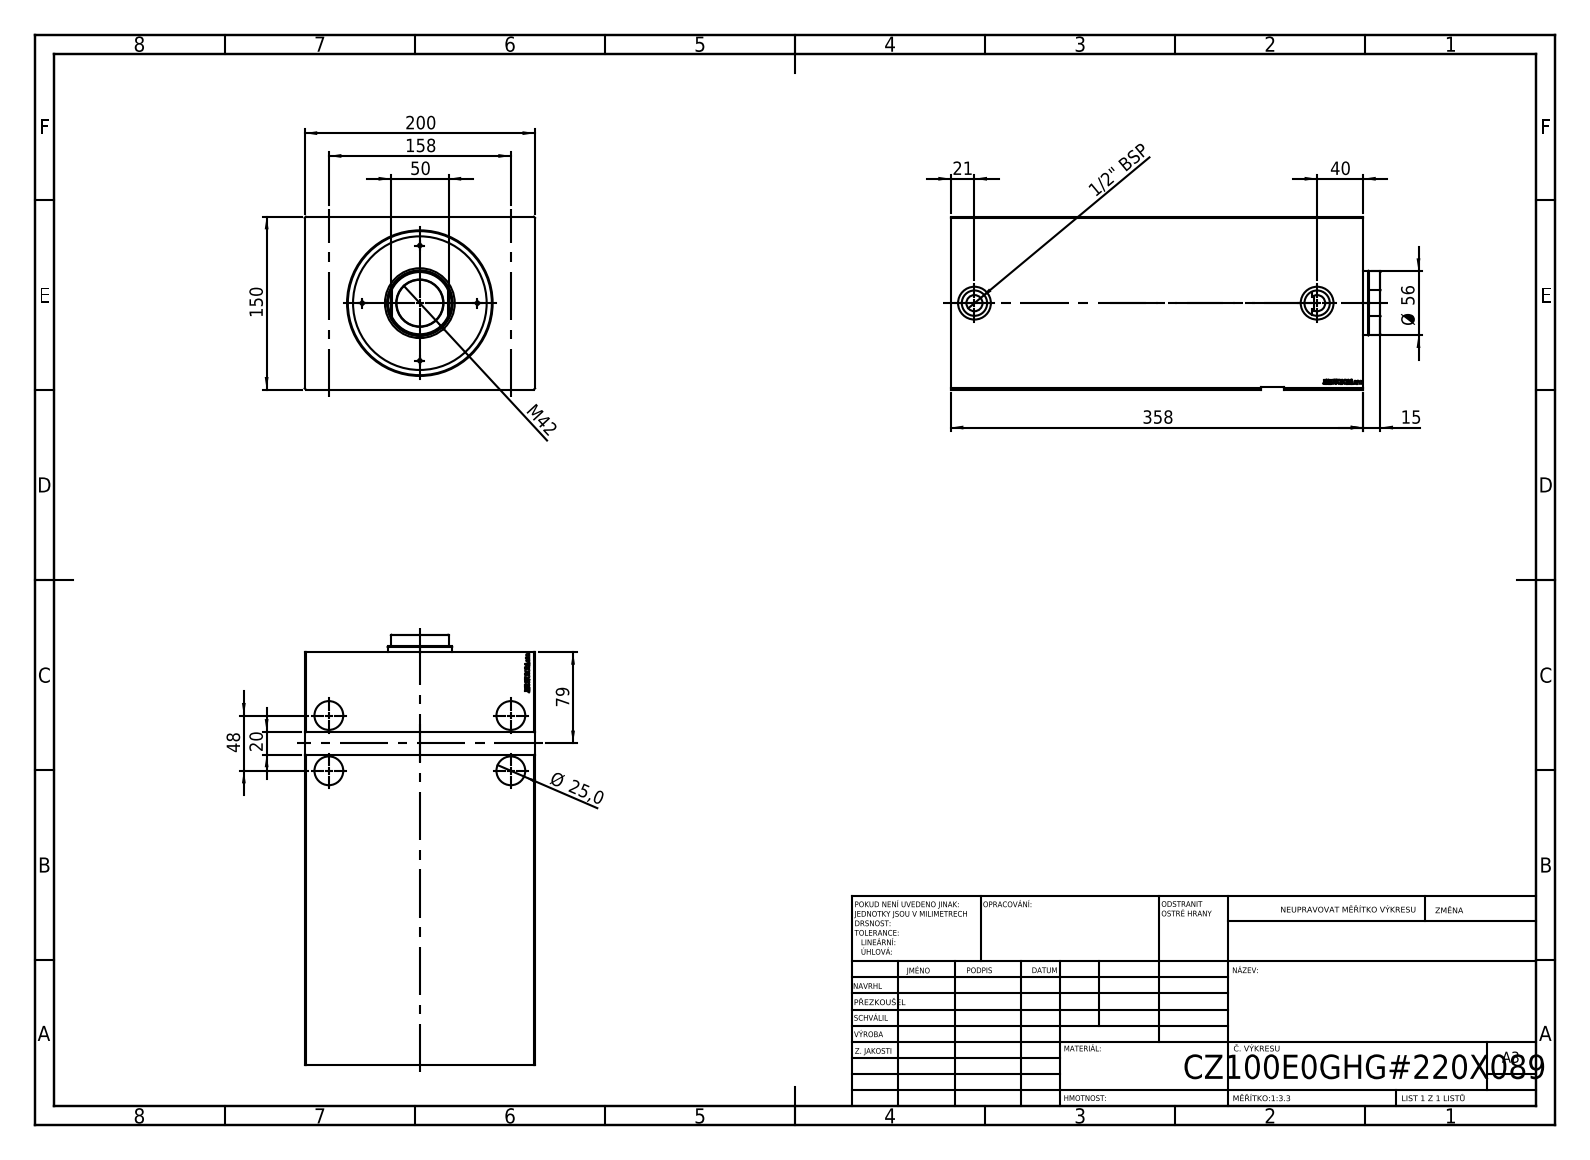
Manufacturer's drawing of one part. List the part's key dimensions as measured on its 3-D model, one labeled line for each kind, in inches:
STEP written by: SolidWorks 2019 (CONFIG_CONTROL_DESIGN)
Units: inches
Bodies: 1 solid, 807 faces (395 planar, 30 cylindrical, 382 other)
Overall size (bounding box): 14.094 × 7.874 × 5.906
Volume: 476.5 in³ · Surface area: 711.4 in²
Round holes (diameter × count): ⌀0.984 ×4, ⌀0.315 ×2, ⌀0.866 ×2, ⌀1.122 ×2, ⌀0.551 ×1, ⌀1.417 ×1, ⌀3.937 ×1, ⌀4.921 ×1
Partial cylindrical surfaces — rounded edges, fillets, slot ends (radius × count): R0.276 ×1
Main face-to-face distances: 5.906, 7.874, 14.094, 12.783, 1.311, 0.591, 12.193, 13.504, 0.079, 5.827
Hole centre spacings: 1.89, 6.22, 6.501, 2.096, 2.951, 4.139, 4.631, 9.081
